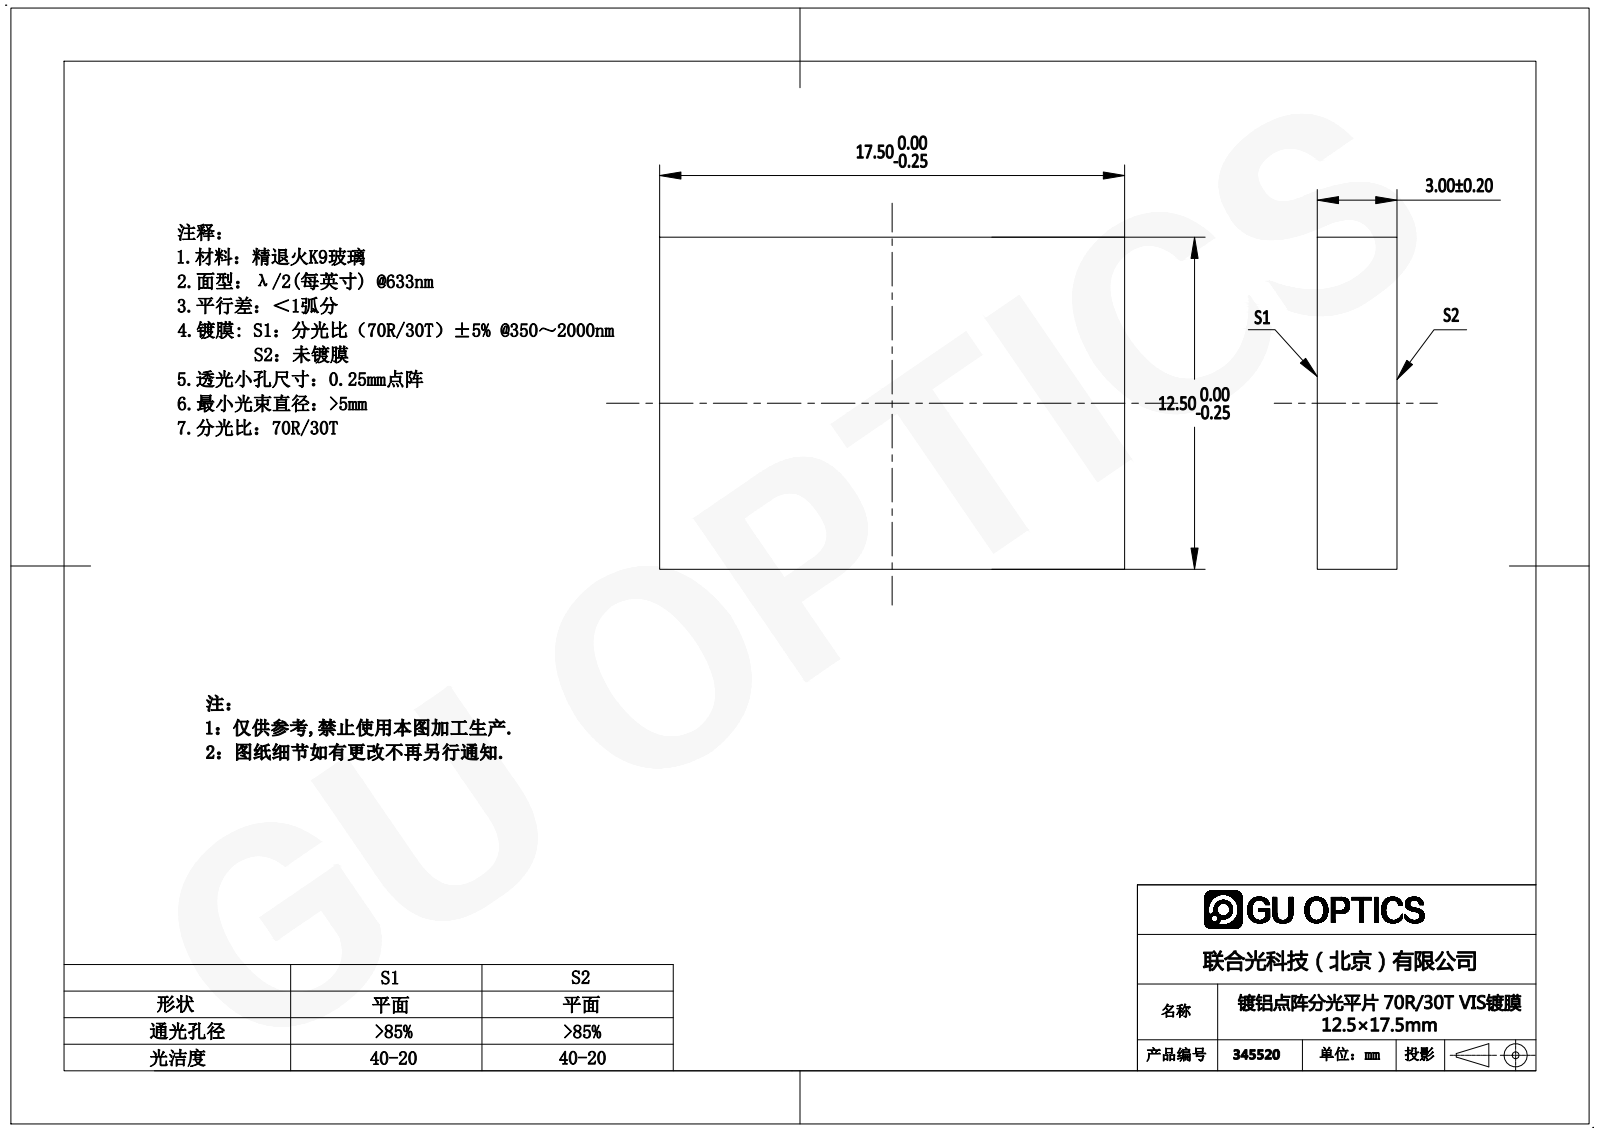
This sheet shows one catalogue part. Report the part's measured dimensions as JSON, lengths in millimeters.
{"part_name": "345502", "step_written_by": "SolidWorks 2016 (AUTOMOTIVE_DESIGN)", "units": "millimeters", "bodies": {"solids": 1, "faces": 6, "planar": 6, "cylindrical": 0, "other": 0}, "overall_size": [17.5, 12.5, 3], "volume_mm3": 656, "surface_area_mm2": 618, "face_to_face_distances": [3, 12.5, 17.5]}
